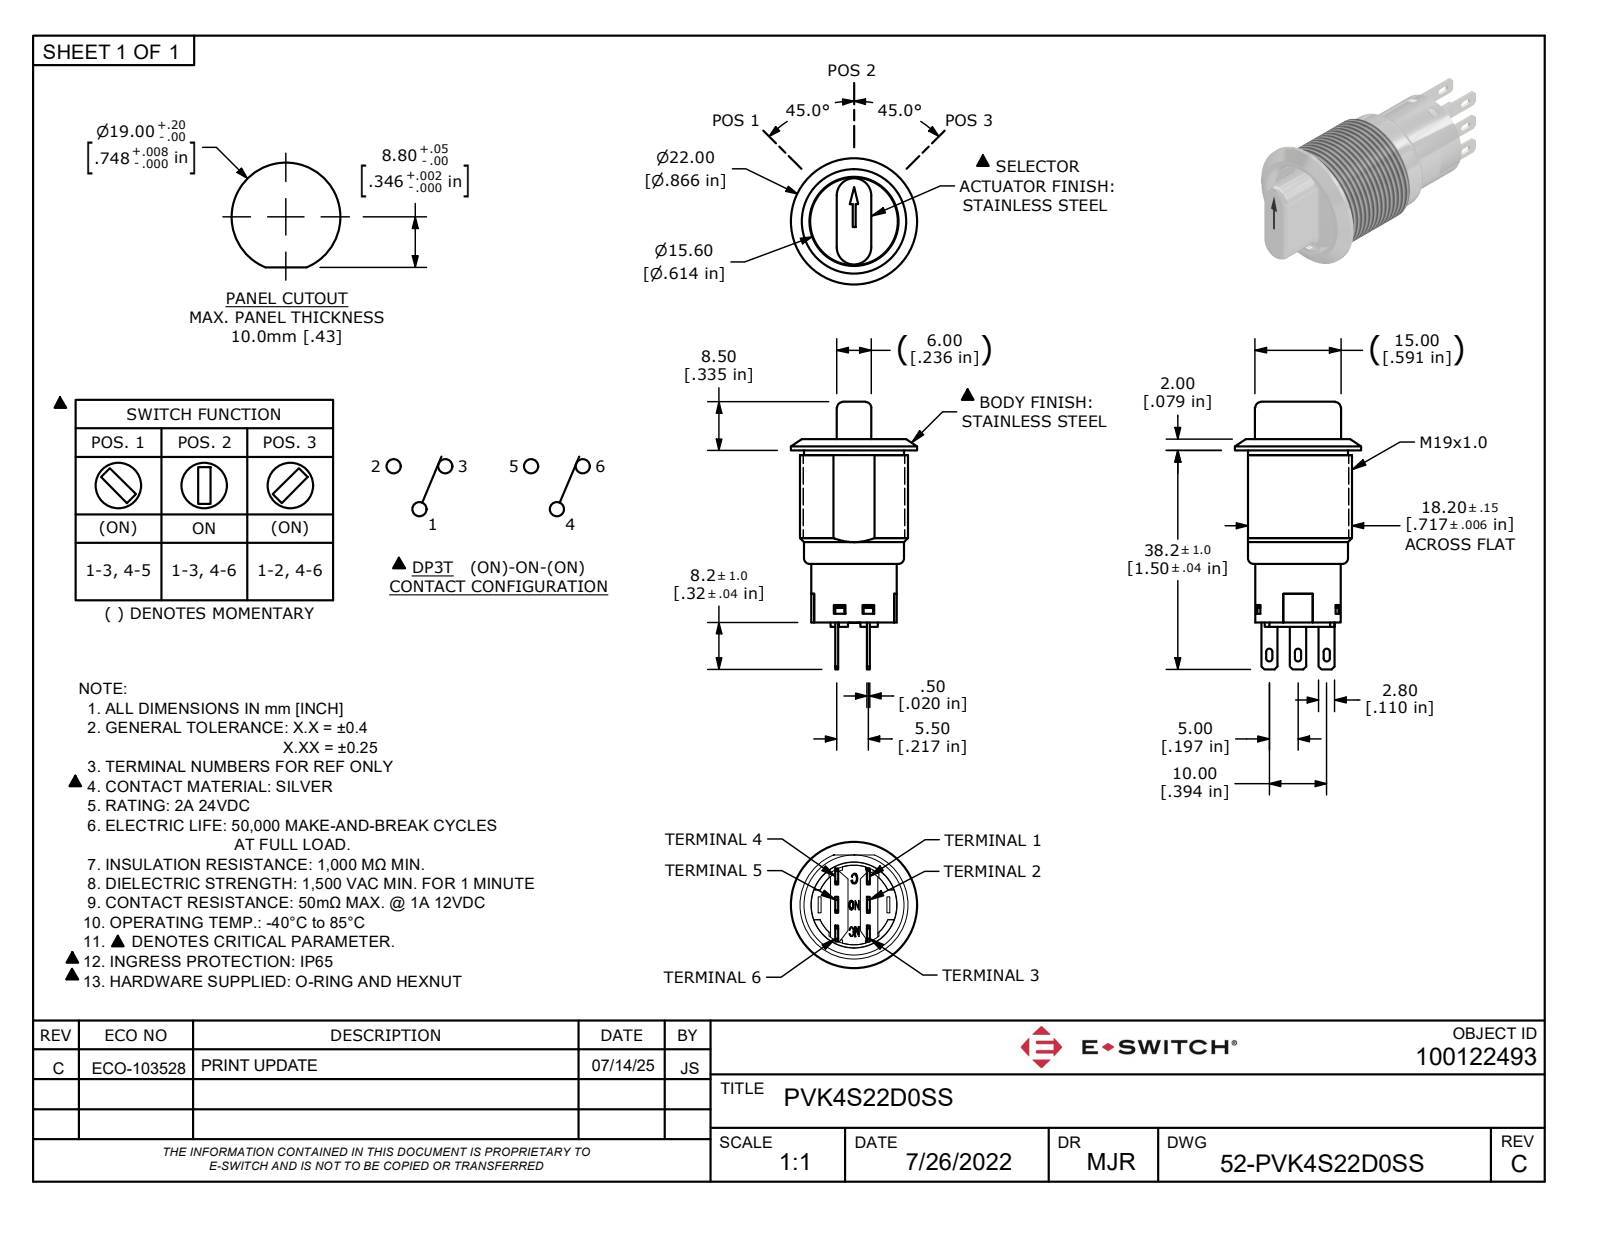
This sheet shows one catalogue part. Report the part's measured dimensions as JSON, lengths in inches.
{"part_name": "PVK4S22D0SS", "step_written_by": "Autodesk Inventor 2022 (AUTOMOTIVE_DESIGN)", "units": "inches", "bodies": {"solids": 2, "faces": 258, "planar": 169, "cylindrical": 45, "other": 44}, "overall_size": [1.87, 0.866, 0.866], "volume_in3": 0.321, "surface_area_in2": 6.936, "round_holes": [[0.591, 1], [0.614, 1]], "round_bosses_or_shafts": [[0.866, 1], [0.689, 1], [0.602, 1], [0.587, 1], [0.571, 1]], "partial_cylinders_radius": [[0.022, 6], [0.02, 2], [0.039, 2], [0.118, 2], [0.254, 1], [0.274, 1], [0.372, 1]], "face_to_face_distances": [0.016, 0.031, 0.618, 0.602, 1.213, 1.181, 0.236, 0.02, 0.217, 0.226]}
